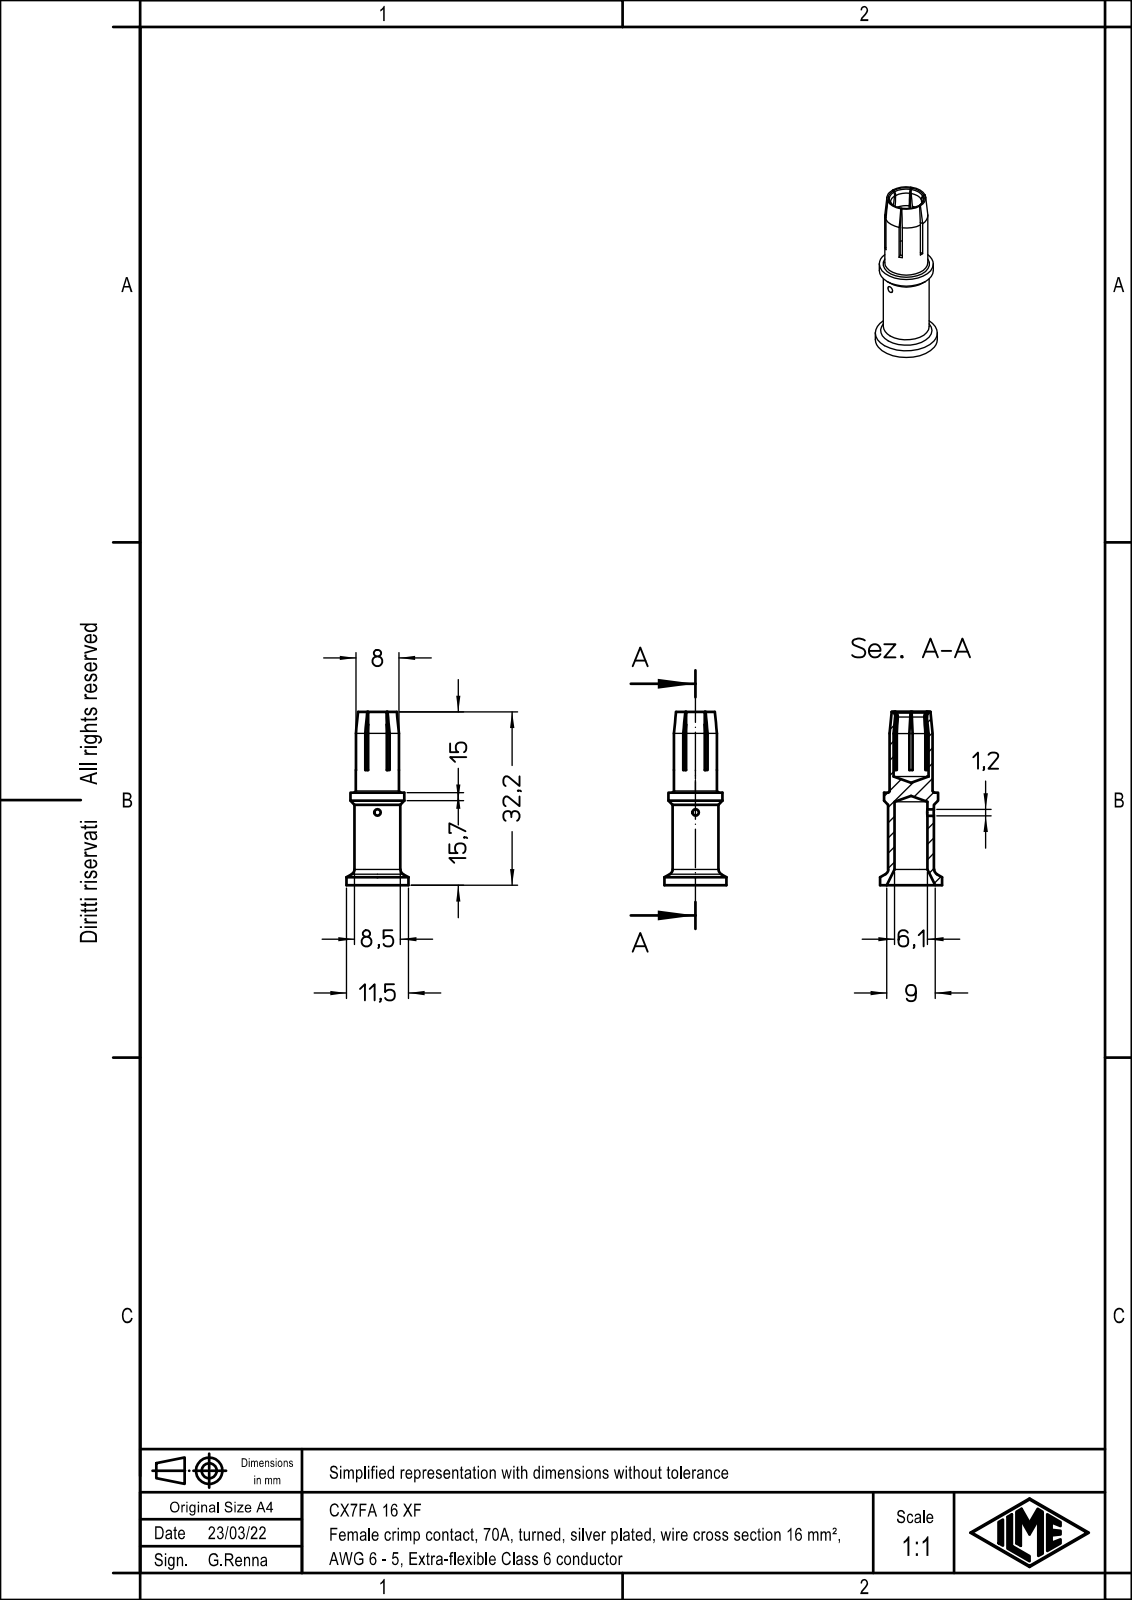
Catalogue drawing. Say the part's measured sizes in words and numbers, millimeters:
The part is named "53962.16XF_F; CX7FA_16_XF". Its 3-D file was written by "Creo Elements/Direct Modeling 20.1B 02-Apr-2019 (C) Parametric Technology GmbH (AUTOMOTIVE_DESIGN)". It is 1 solid with 90 faces: 32 planar, 14 cylindrical and 44 other. Overall it measures 32.2 by 11.5 by 11.5 millimeters. Its volume is 907 cubic millimeters and its surface area 1 623 square millimeters. Round holes: 1 of diameter 1.2, 1 of diameter 6.1, 1 of diameter 6.5. Round bosses or shafts: 1 of diameter 11.5, 1 of diameter 10, 1 of diameter 8.5, 1 of diameter 8. The main face-to-face distances are 0.6, 17.2, 4.2, 21.4.
